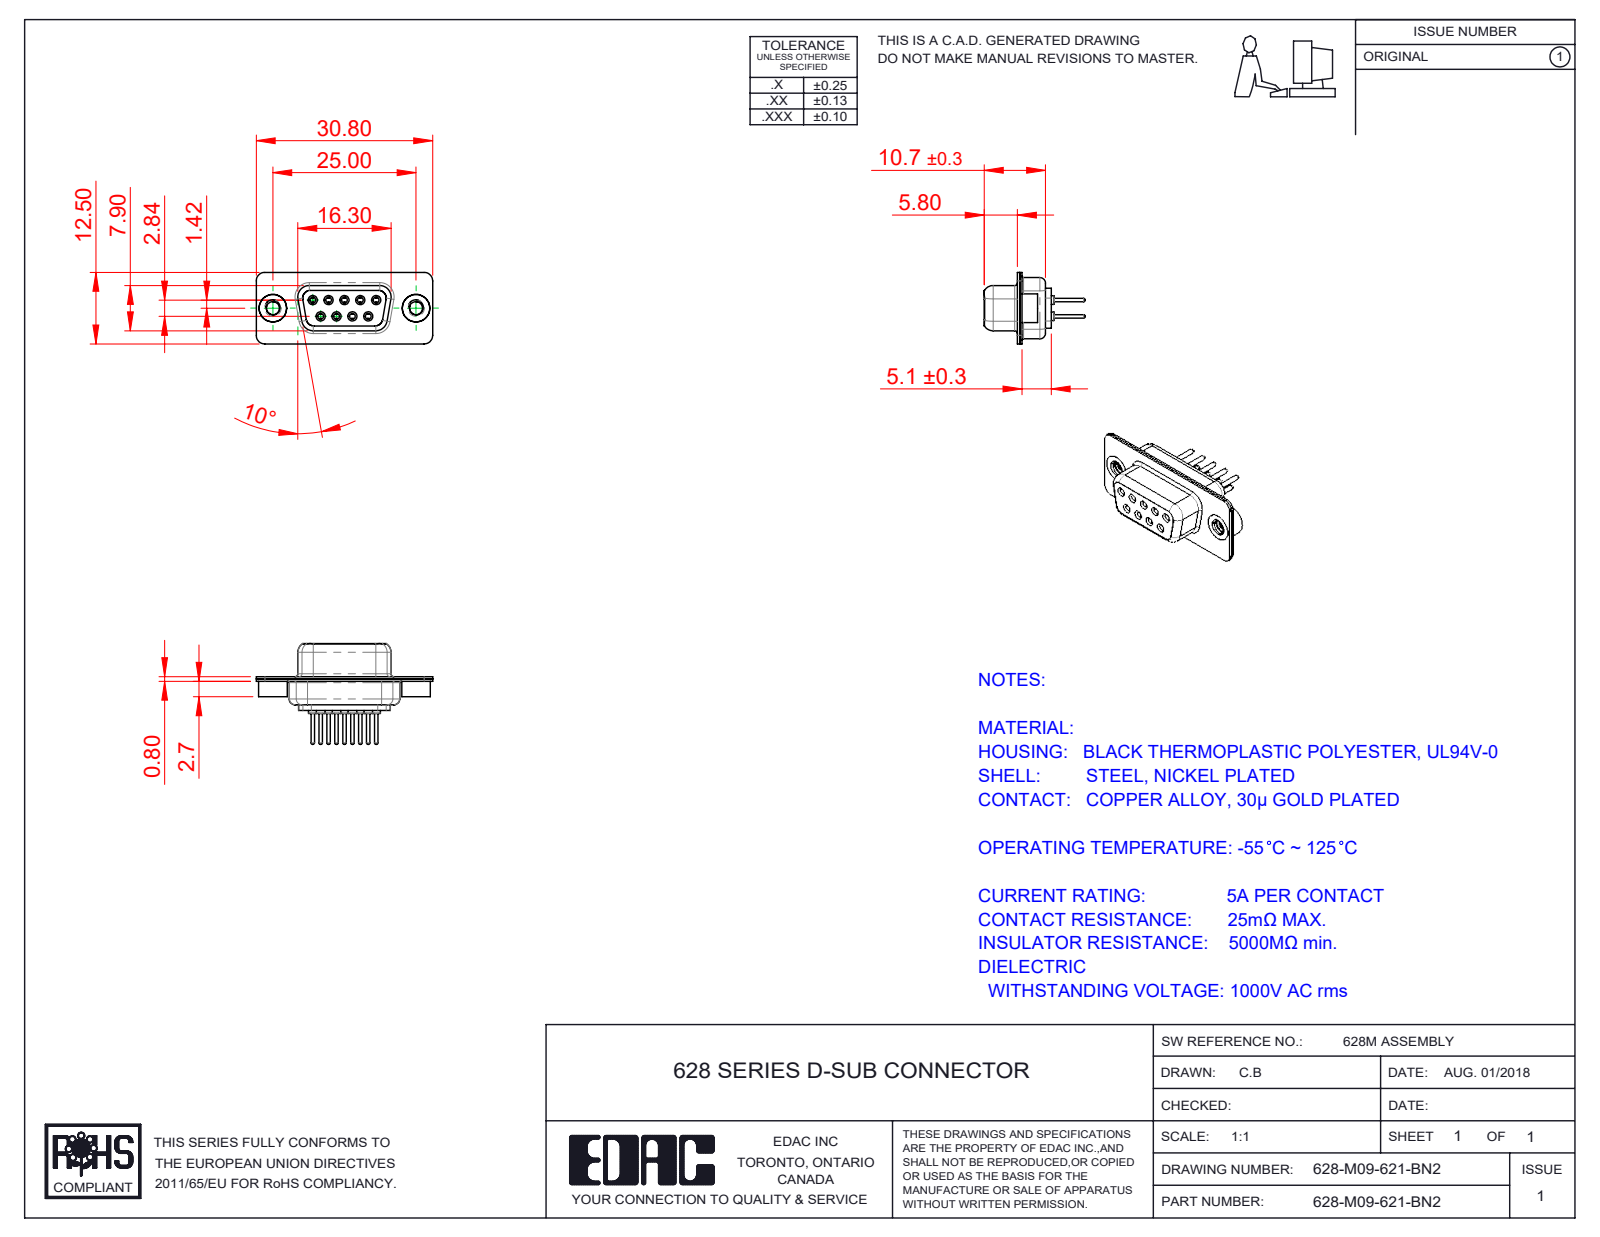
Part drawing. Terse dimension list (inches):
name: 628M 4-40 Threaded Rivet; 628M Contact Row 1_21; 628M Contact Row 2_21; 628M Shell Front_09 Contacts (+3 more)
written by: SolidWorks 2020 (CONFIG_CONTROL_DESIGN)
unit: in
bodies: 14 solids, 774 faces (202 planar, 308 cylindrical, 264 other)
size: 1.213 × 0.693 × 0.492
volume: 0.104 in³; area: 6.862 in²
holes: 9× ⌀0.039, 9× ⌀0.043, 9× ⌀0.067, 9× ⌀0.071, 9× ⌀0.079, 2× ⌀0.089, 2× ⌀0.157, 2× ⌀0.189
bosses: 9× ⌀0.087, 9× ⌀0.063, 9× ⌀0.059, 9× ⌀0.024, 2× ⌀0.197, 2× ⌀0.193
rounds: 16× R0.059, 12× R0.079, 8× R0.053, 8× R0.063, 4× R0.01, 4× R0.02, 4× R0.024, 4× R0.026
face distances: 0.016, 0.055, 0.018, 0.333, 0.031, 0.039, 0.35, 0.071, 0.244, 0.278
hole spacings: 0.124, 0.109, 0.218, 0.198, 0.198, 0.327, 0.28, 0.294
